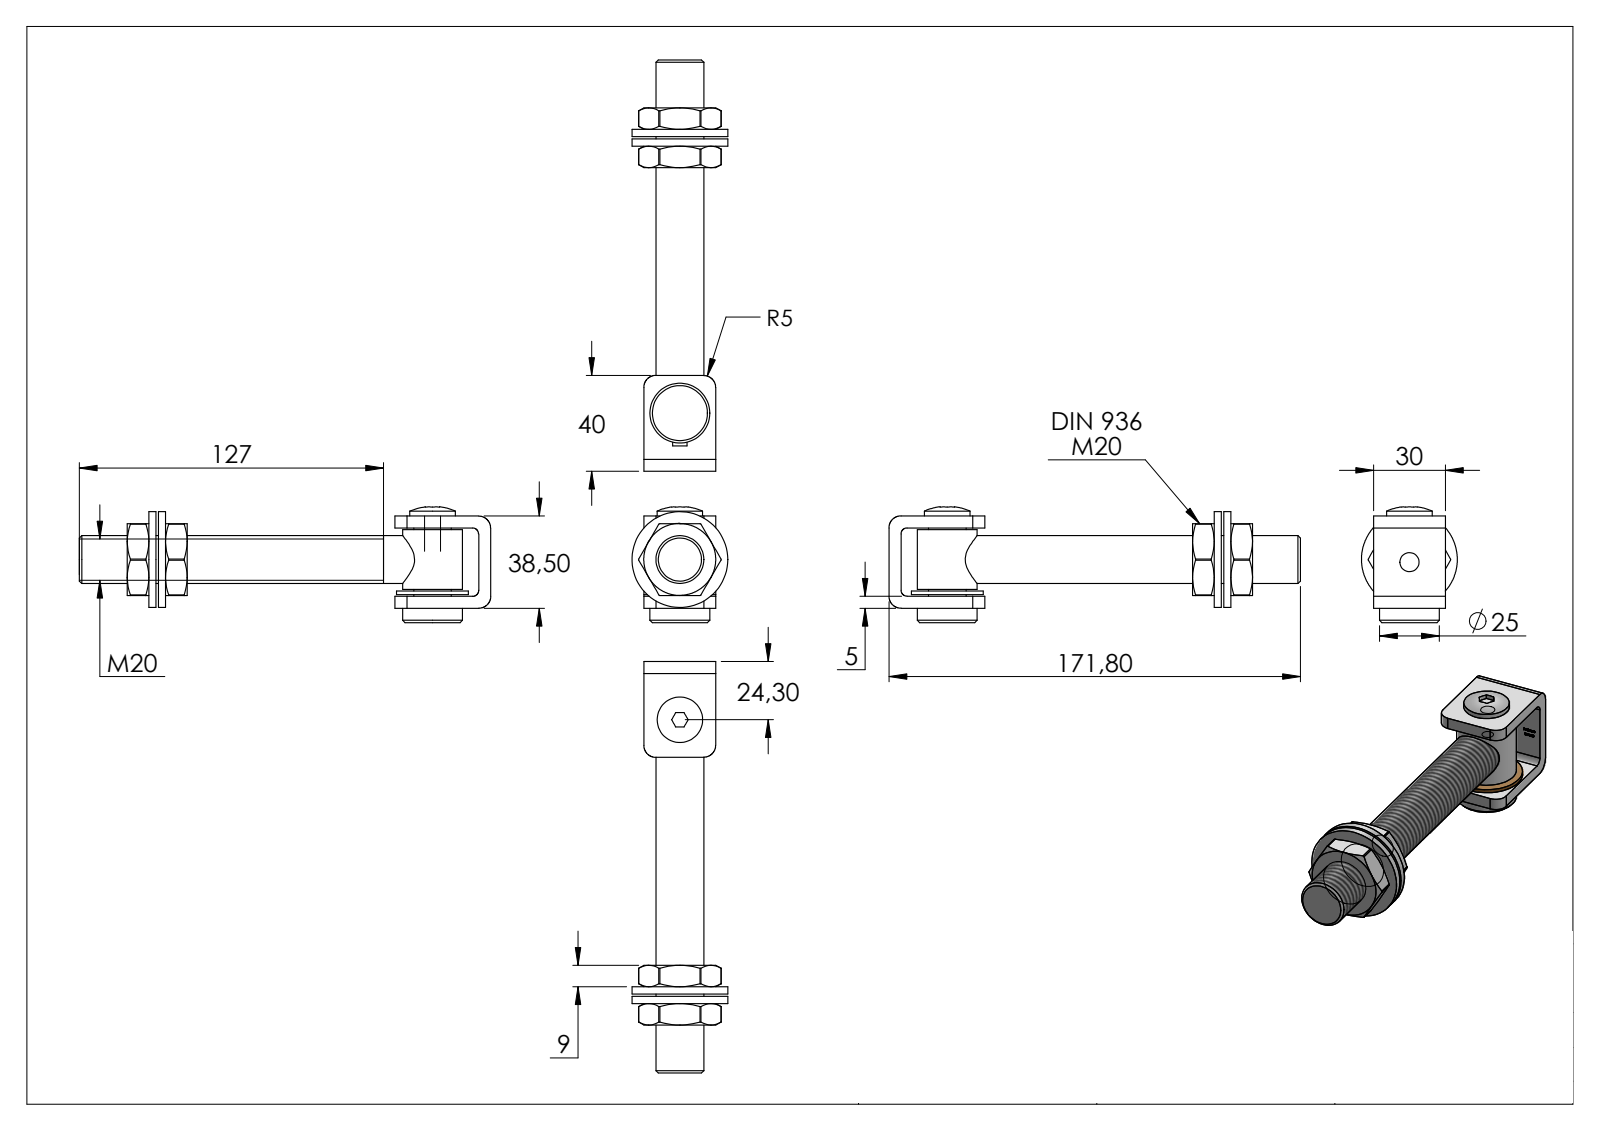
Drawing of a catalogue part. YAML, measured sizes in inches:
part_name: "Torband Teil1_130-M20 Teil1; Torband Teil1; 130-Mxx Teil6; Torband Teil5_130-M20 Teil5 (+8 more)"
step_written_by: "SolidWorks 2018 (CONFIG_CONTROL_DESIGN)"
units: inches
bodies: {solids: 9, faces: 394, planar: 184, cylindrical: 58, other: 152}
overall_size: [866.142, 826.772, 826.772]
volume: 5.465
surface_area: 55.05
round_holes:
  - {diameter: 0.268, count: 1}
  - {diameter: 0.315, count: 1}
  - {diameter: 0.65, count: 1}
  - {diameter: 0.689, count: 1}
  - {diameter: 0.827, count: 1}
round_bosses_or_shafts:
  - {diameter: 1.575, count: 1}
  - {diameter: 1.181, count: 1}
  - {diameter: 0.984, count: 1}
  - {diameter: 0.787, count: 1}
  - {diameter: 0.748, count: 1}
  - {diameter: 0.618, count: 1}
  - {diameter: 0.315, count: 1}
partial_cylinders:
  - {radius: 0.02, count: 6}
  - {radius: 0.197, count: 4}
  - {radius: 0.098, count: 2}
face_to_face_distances: [0.197, 0.157, 0.118, 1.319, 0.276, 1.181, 1.516, 0.472, 0.039, 0.354]
hole_center_spacings: [0.043]
